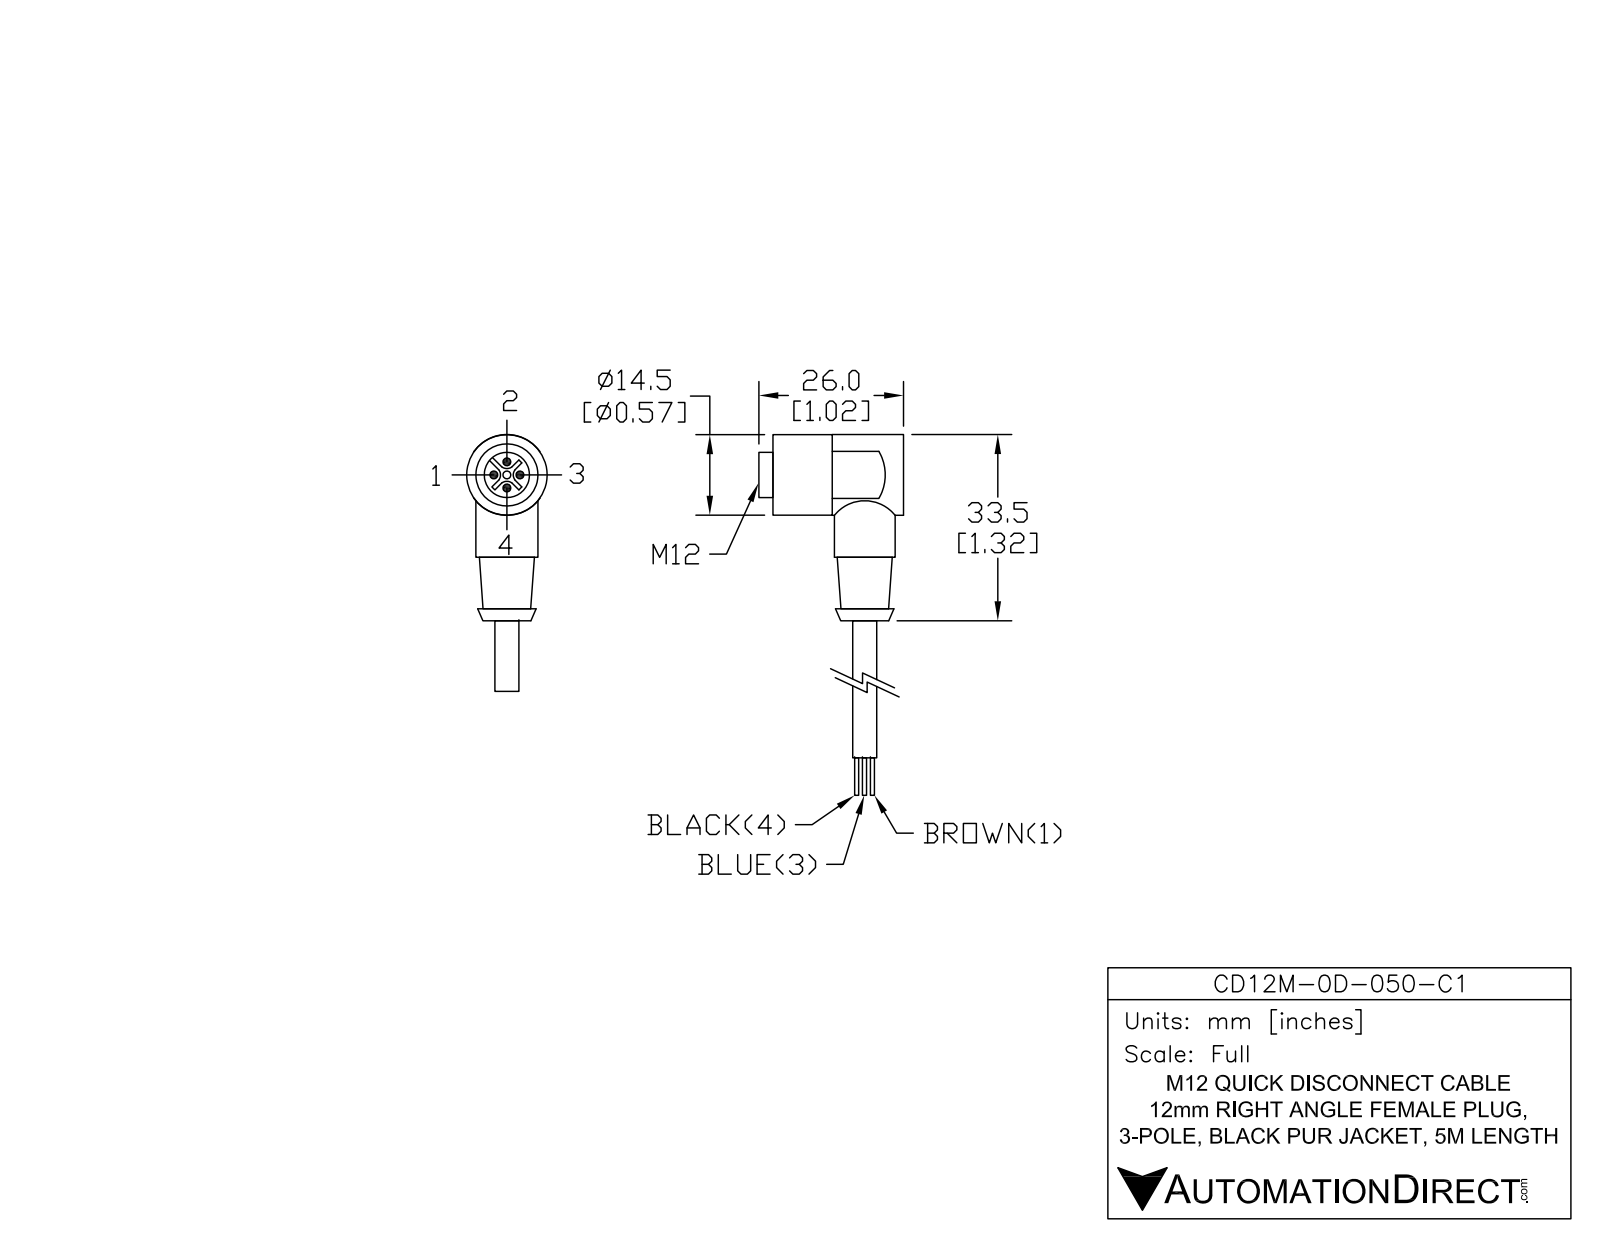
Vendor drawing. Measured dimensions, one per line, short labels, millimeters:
name: CD12M-0D-050-C1
written by: SolidWorks 2017 (AUTOMOTIVE_DESIGN)
unit: mm
bodies: 4 solids, 326 faces (218 planar, 106 cylindrical, 2 other)
size: 140.3 × 27.5 × 14.9
volume: 8 514 mm³; area: 5 495 mm²
holes: 5× ⌀1, 1× ⌀8.5, 1× ⌀12
bosses: 1× ⌀14.9, 1× ⌀10.4, 1× ⌀8.7, 1× ⌀8.1, 1× ⌀4.9
rounds: 1× R0.55
face distances: 13.7, 12.7, 1, 1.4, 15.1, 2.4, 16.7, 5.9, 25.6, 12.9
hole spacings: 2.35, 3.32, 4.7
